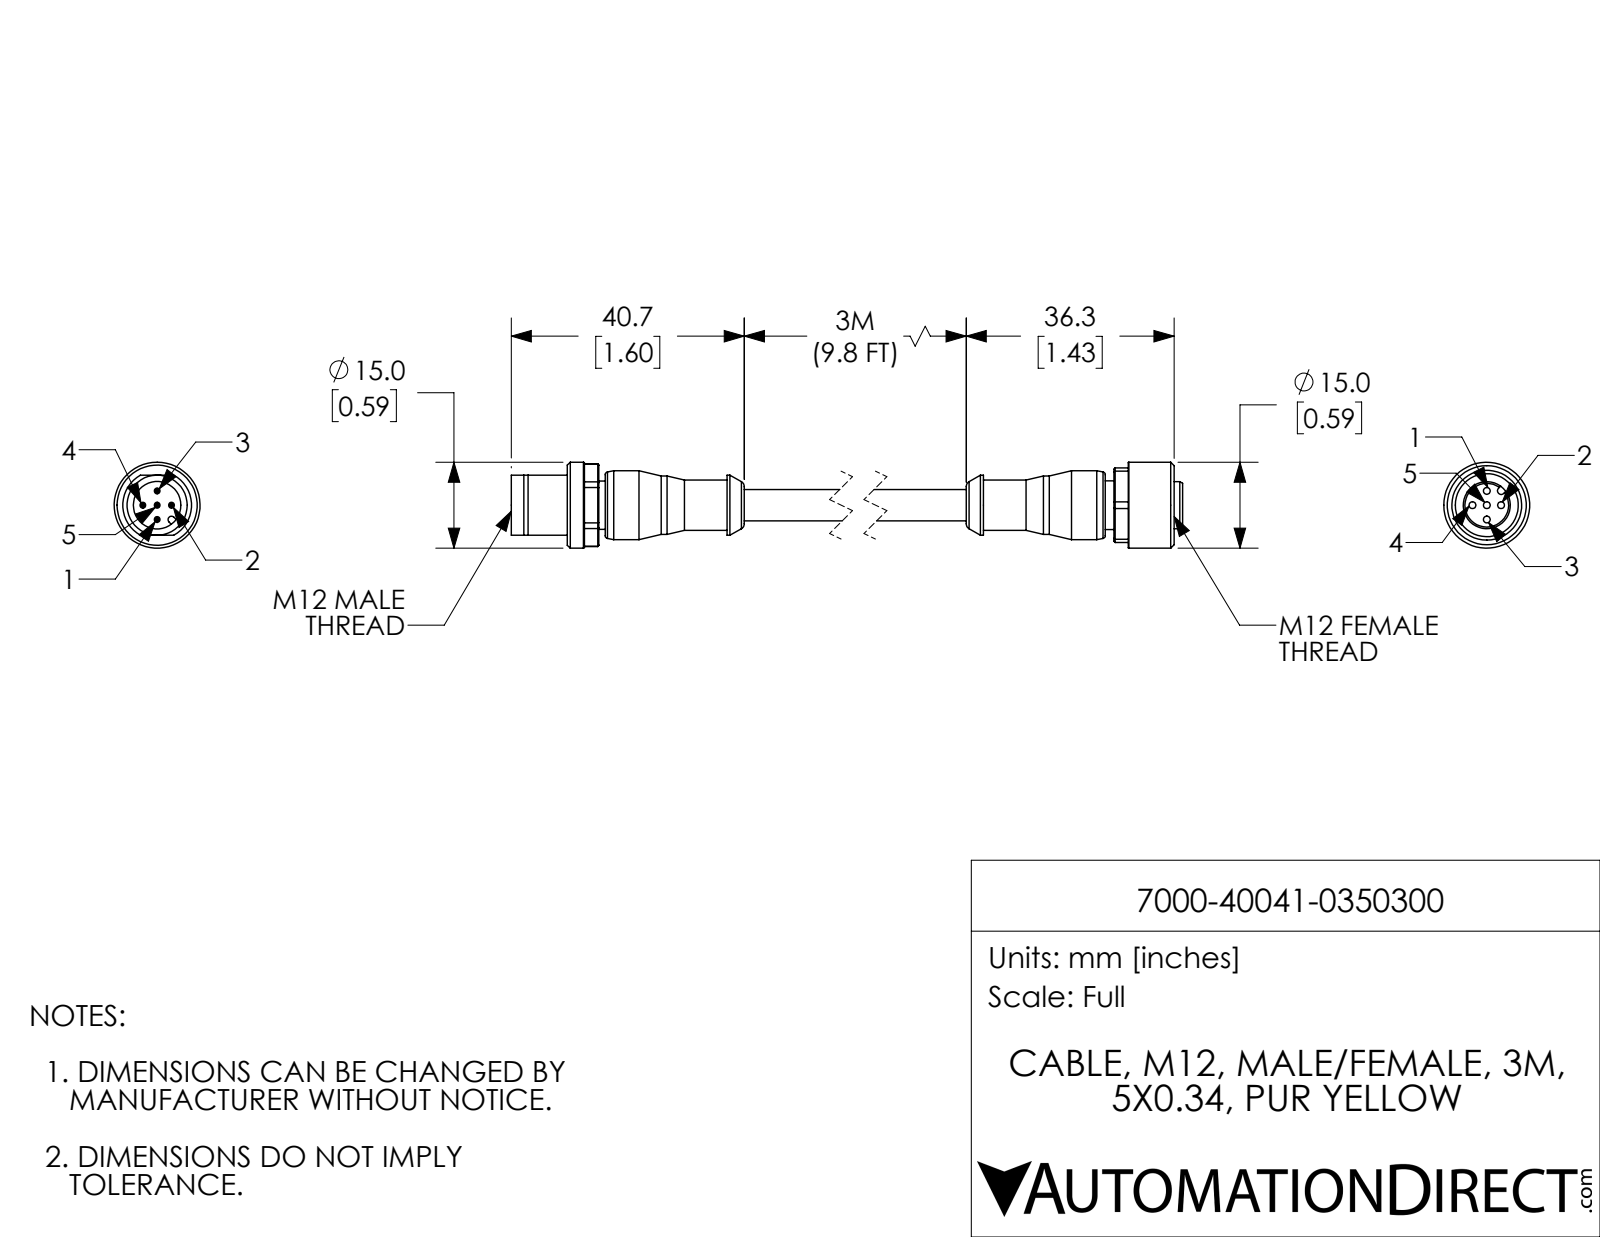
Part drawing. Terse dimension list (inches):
name: 7000-40041-0350300_FEMALE; 7000-40041-0350300; 7000-40041-0350300_MALE
written by: SolidWorks 2021 (CONFIG_CONTROL_DESIGN)
unit: in
bodies: 2 solids, 196 faces (60 planar, 73 cylindrical, 63 other)
size: 5.138 × 0.591 × 0.591
volume: 0.488 in³; area: 8.004 in²
holes: 5× ⌀0.047, 1× ⌀0.327, 1× ⌀0.433
bosses: 5× ⌀0.039, 1× ⌀0.591, 1× ⌀0.472, 1× ⌀0.413, 1× ⌀0.402, 1× ⌀0.346, 1× ⌀0.335, 1× ⌀0.331
rounds: 1× R0.024, 1× R0.026, 1× R0.283
face distances: 0.472, 0.512, 0.118, 4.063, 0.413, 4.433, 2.217, 4.28, 0.295, 0.059
hole spacings: 0.098, 0.139, 0.197
